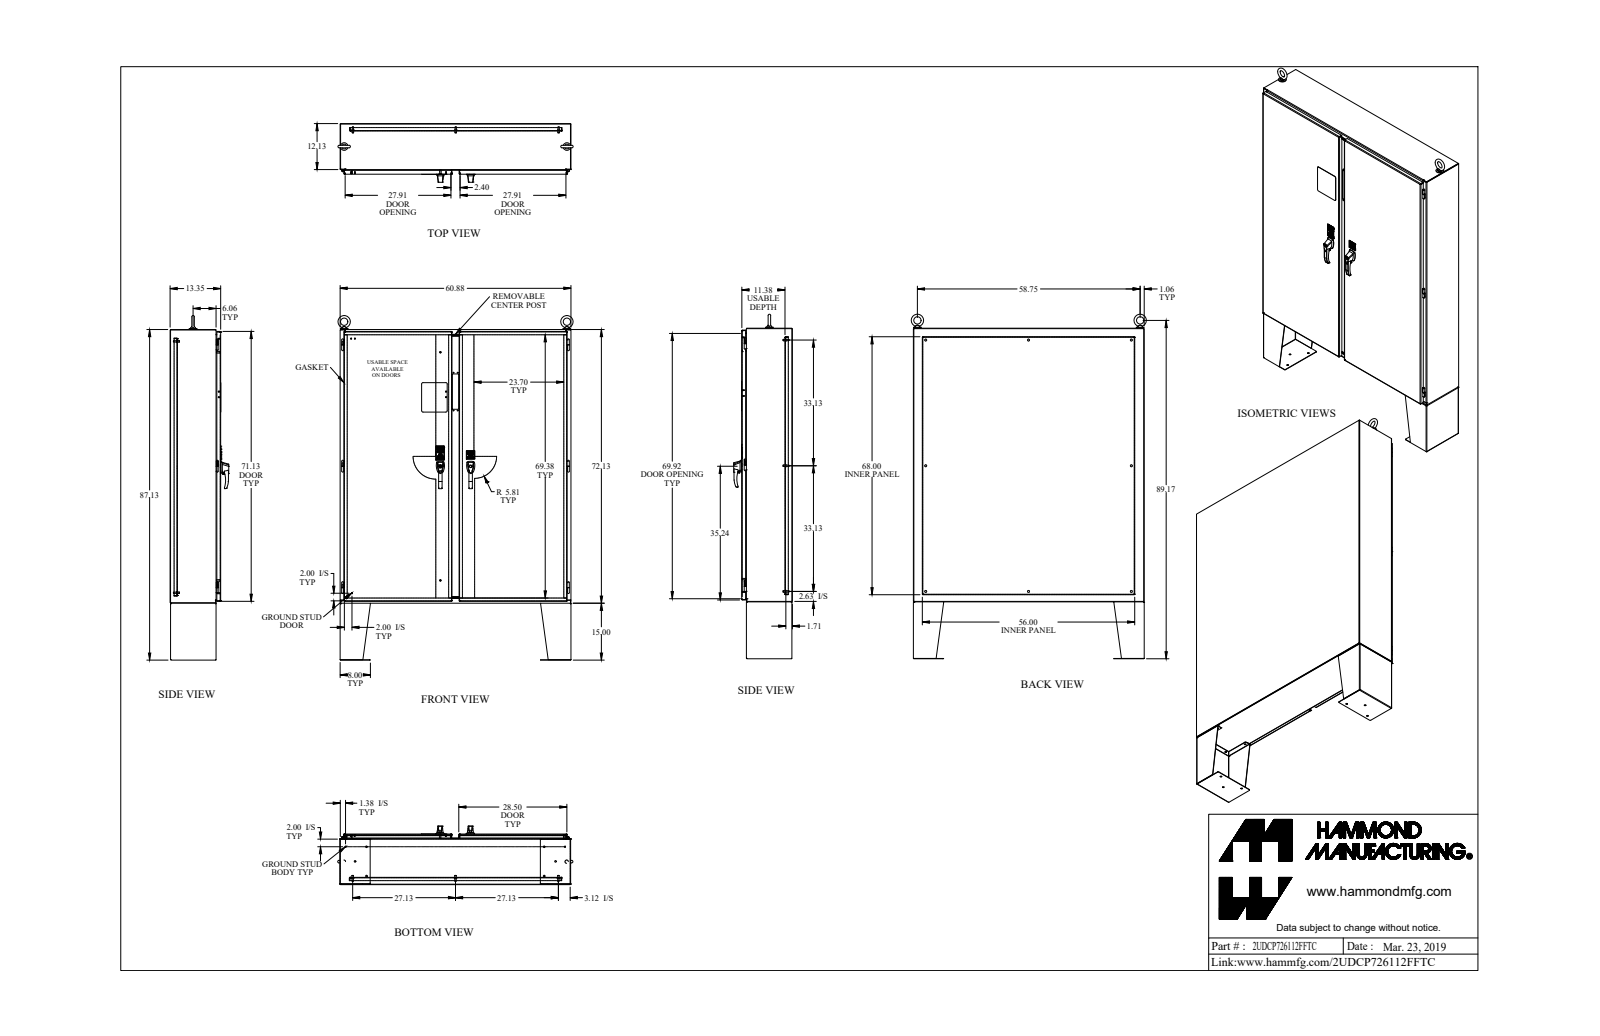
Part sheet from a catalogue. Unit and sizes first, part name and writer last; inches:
Units: inches
Overall size (bounding box): 90.799 × 61.997 × 15.465
Round holes (diameter × count): ⌀0.437 ×14, ⌀0.307 ×10, ⌀0.281 ×9, ⌀0.25 ×8, ⌀0.35 ×8, ⌀0.313 ×6, ⌀0.196 ×5, ⌀0.445 ×5, ⌀0.257 ×4, ⌀0.28 ×4, ⌀0.39 ×4, ⌀0.413 ×4
Round bosses / shafts (diameter × count): ⌀0.25 ×14, ⌀1 ×12, ⌀0.375 ×9, ⌀0.65 ×8, ⌀0.33 ×8, ⌀0.281 ×8, ⌀0.625 ×5, ⌀0.75 ×4
Partial cylindrical surfaces — rounded edges, fillets, slot ends (radius × count): R0.06 ×54, R0.125 ×44, R0.5 ×38, R0.017 ×32, R0.185 ×29, R0.048 ×16, R0.143 ×16, R0.03 ×12
Main face-to-face distances: 0.125, 0.072, 11.431, 13.368, 13.243, 1.937, 1.812, 1.865, 1.741, 11.503
Hole centre spacings: 7.996, 1.287, 4.888, 6.228, 7.456, 8.074, 9.964, 10.99
Volume: 3 951 in³ · Surface area: 40 863 in²
Bodies: 178 solids, 2694 faces (1564 planar, 810 cylindrical, 320 other)
Part name (STEP PRODUCT): 2UDCP726112FFTC
STEP written by: SolidWorks 2018 (AUTOMOTIVE_DESIGN)
